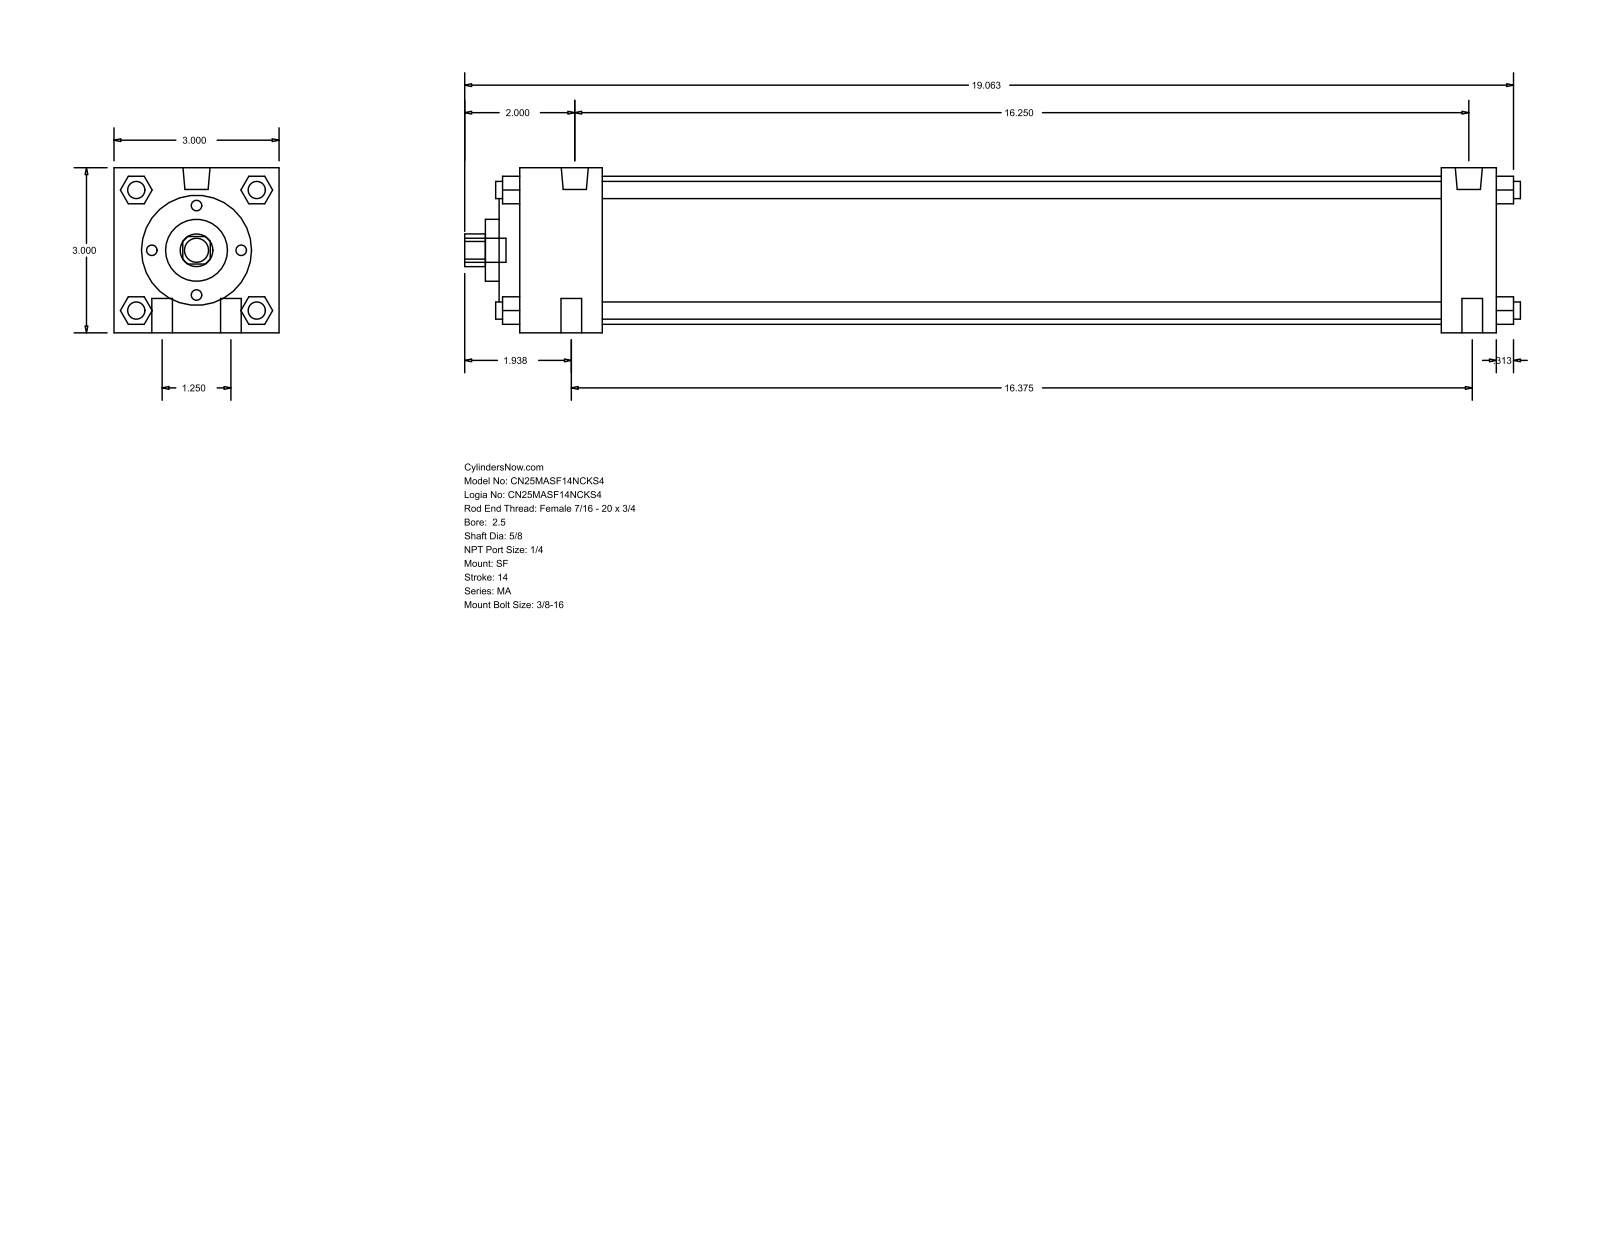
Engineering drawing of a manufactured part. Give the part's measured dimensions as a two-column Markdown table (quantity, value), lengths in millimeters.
| quantity | value |
| --- | --- |
| part name | MA_SF__0250_0.625 |
| STEP written by | GSSL Pune (CONFIG_CONTROL_DESIGN) |
| units | millimeters |
| bodies | 0 solids, 126 faces (95 planar, 31 cylindrical, 0 other) |
| overall size | 487.36 × 76.2 × 76.2 |
| round holes (diameter × count) | 15.88 × 1, 28.57 × 1, 50.8 × 1, 68.33 × 1 |
| round bosses / shafts (diameter × count) | 7.94 × 6, 9.53 × 4, 12.49 × 2, 11.11 × 1 |
| partial cylindrical surfaces (radius × count) | 7.54 × 1 |
| main face-to-face distances | 76.2, 450.85, 25.4, 425.45, 38.1, 387.35, 412.75, 12.7, 9.52, 47.62 |
